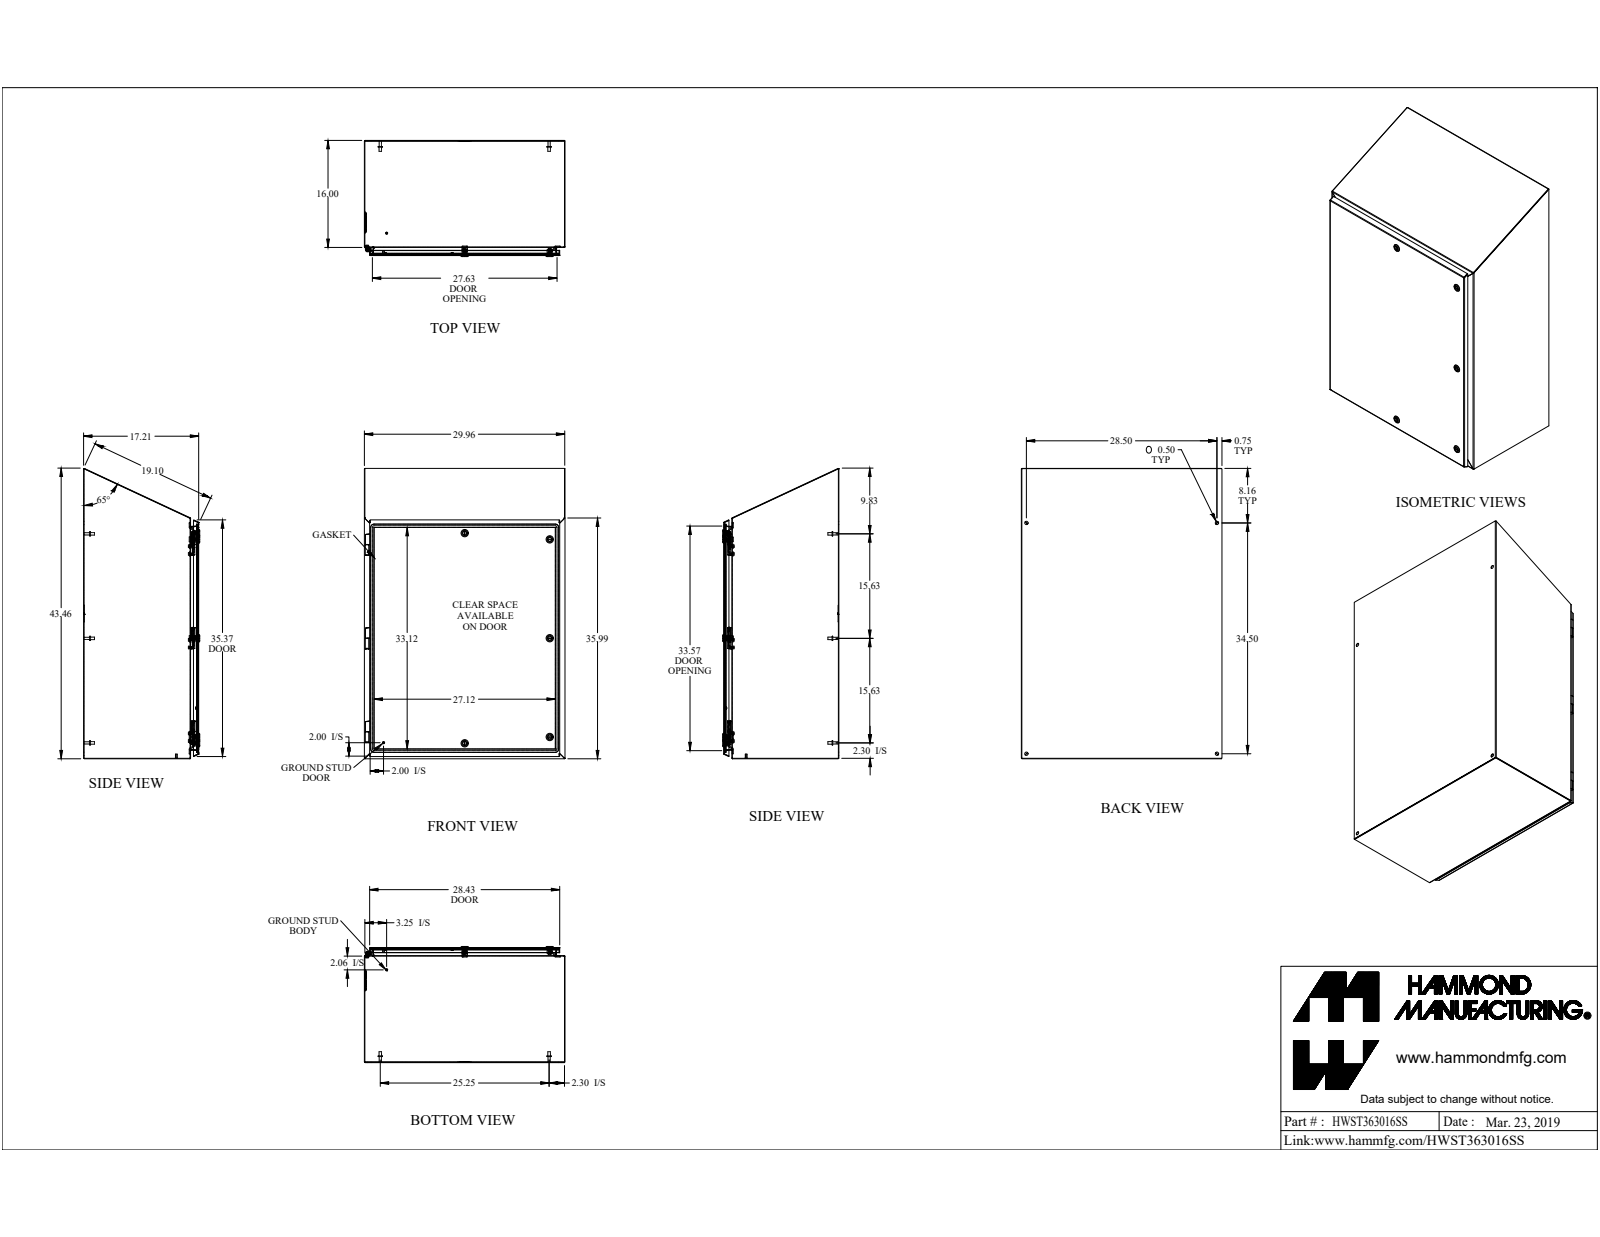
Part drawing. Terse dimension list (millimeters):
name: HWST363016S16
written by: SolidWorks 2019 (AUTOMOTIVE_DESIGN)
unit: mm
bodies: 71 solids, 1628 faces (1014 planar, 428 cylindrical, 186 other)
size: 1102.6 × 762 × 441.2
volume: 6 261 000 mm³; area: 6 748 000 mm²
holes: 12× ⌀4.9, 12× ⌀6.1, 9× ⌀12.7, 6× ⌀7, 5× ⌀5, 5× ⌀9.8, 5× ⌀16, 5× ⌀19.5, 2× ⌀3.3, 1× ⌀6.1, 1× ⌀88.9
bosses: 12× ⌀5.7, 11× ⌀15.9, 6× ⌀16.5, 6× ⌀9.5, 6× ⌀8.4, 6× ⌀6, 5× ⌀27.9, 5× ⌀19.9
rounds: 24× R1, 24× R6.4, 22× R3.2, 17× R0.9, 17× R2.7, 16× R0.3, 16× R0.8, 6× R3.4
face distances: 1.8, 1.8, 433.5, 435.3, 435.3, 437.1, 758.3, 760.2, 760.2, 762
hole spacings: 29, 355.3, 355.3, 355.3, 710.5, 326.3, 384.3, 29
